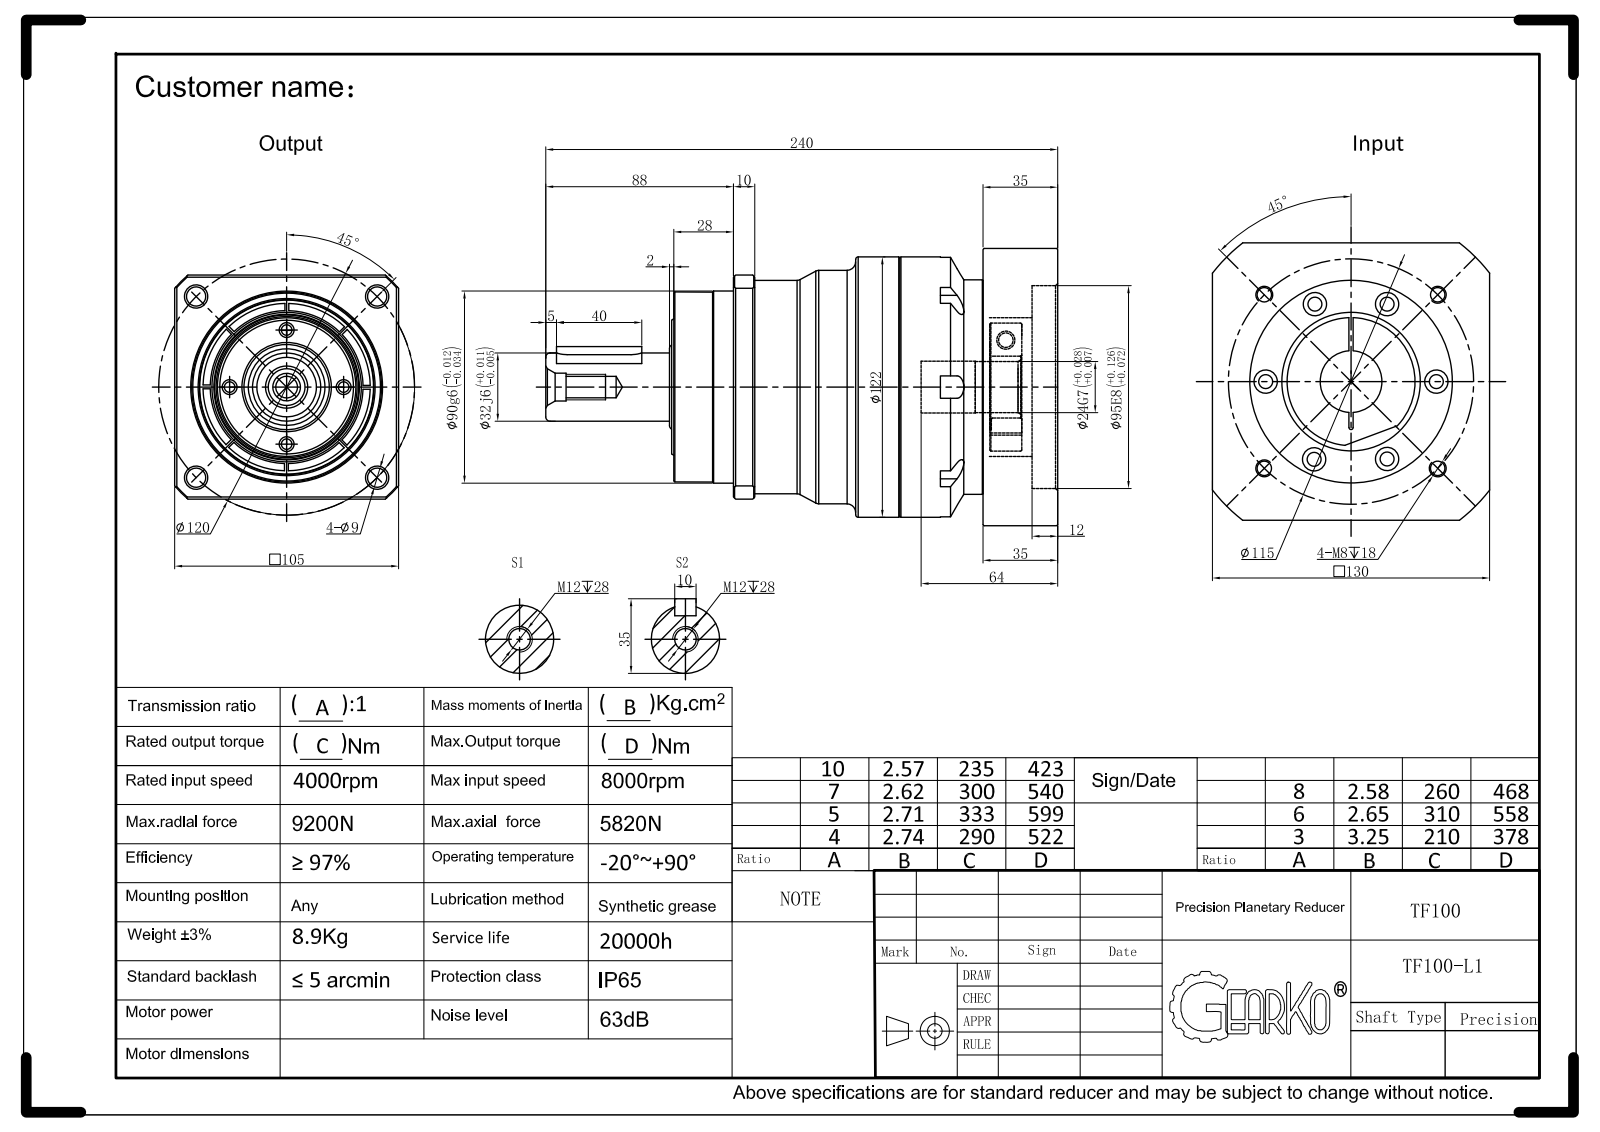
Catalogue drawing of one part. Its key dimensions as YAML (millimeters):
part_name: "TF100-010-05-001; TF100-000-03-001; TB115-000-12-001; 115-19-95-115 (+3 more)"
step_written_by: "SolidWorks 2017 (CONFIG_CONTROL_DESIGN)"
units: millimeters
bodies: {solids: 6, faces: 544, planar: 122, cylindrical: 197, other: 225}
overall_size: [239.8, 130, 130]
volume: 1627000
surface_area: 210662
round_holes:
  - {diameter: 5, count: 14}
  - {diameter: 6.5, count: 8}
  - {diameter: 6.6, count: 6}
  - {diameter: 10.5, count: 6}
  - {diameter: 6.8, count: 5}
  - {diameter: 9, count: 4}
  - {diameter: 8.5, count: 1}
  - {diameter: 10.2, count: 1}
  - {diameter: 13, count: 1}
  - {diameter: 13.3, count: 1}
  - {diameter: 14, count: 1}
  - {diameter: 24, count: 1}
round_bosses_or_shafts:
  - {diameter: 122, count: 1}
  - {diameter: 109.4, count: 1}
  - {diameter: 100.5, count: 1}
  - {diameter: 100, count: 1}
  - {diameter: 90, count: 1}
  - {diameter: 89, count: 1}
  - {diameter: 83, count: 1}
  - {diameter: 40, count: 1}
partial_cylinders:
  - {radius: 5.25, count: 8}
  - {radius: 5, count: 2}
  - {radius: 0.75, count: 1}
  - {radius: 1, count: 1}
  - {radius: 52.61, count: 1}
  - {radius: 70, count: 1}
  - {radius: 82.5, count: 1}
face_to_face_distances: [35, 39, 74, 3, 42, 32, 130, 105.6, 144.6, 147.6]
hole_center_spacings: [81.41, 56.51, 95.66, 98.59, 33.41, 43.28, 81.73, 104.4]
